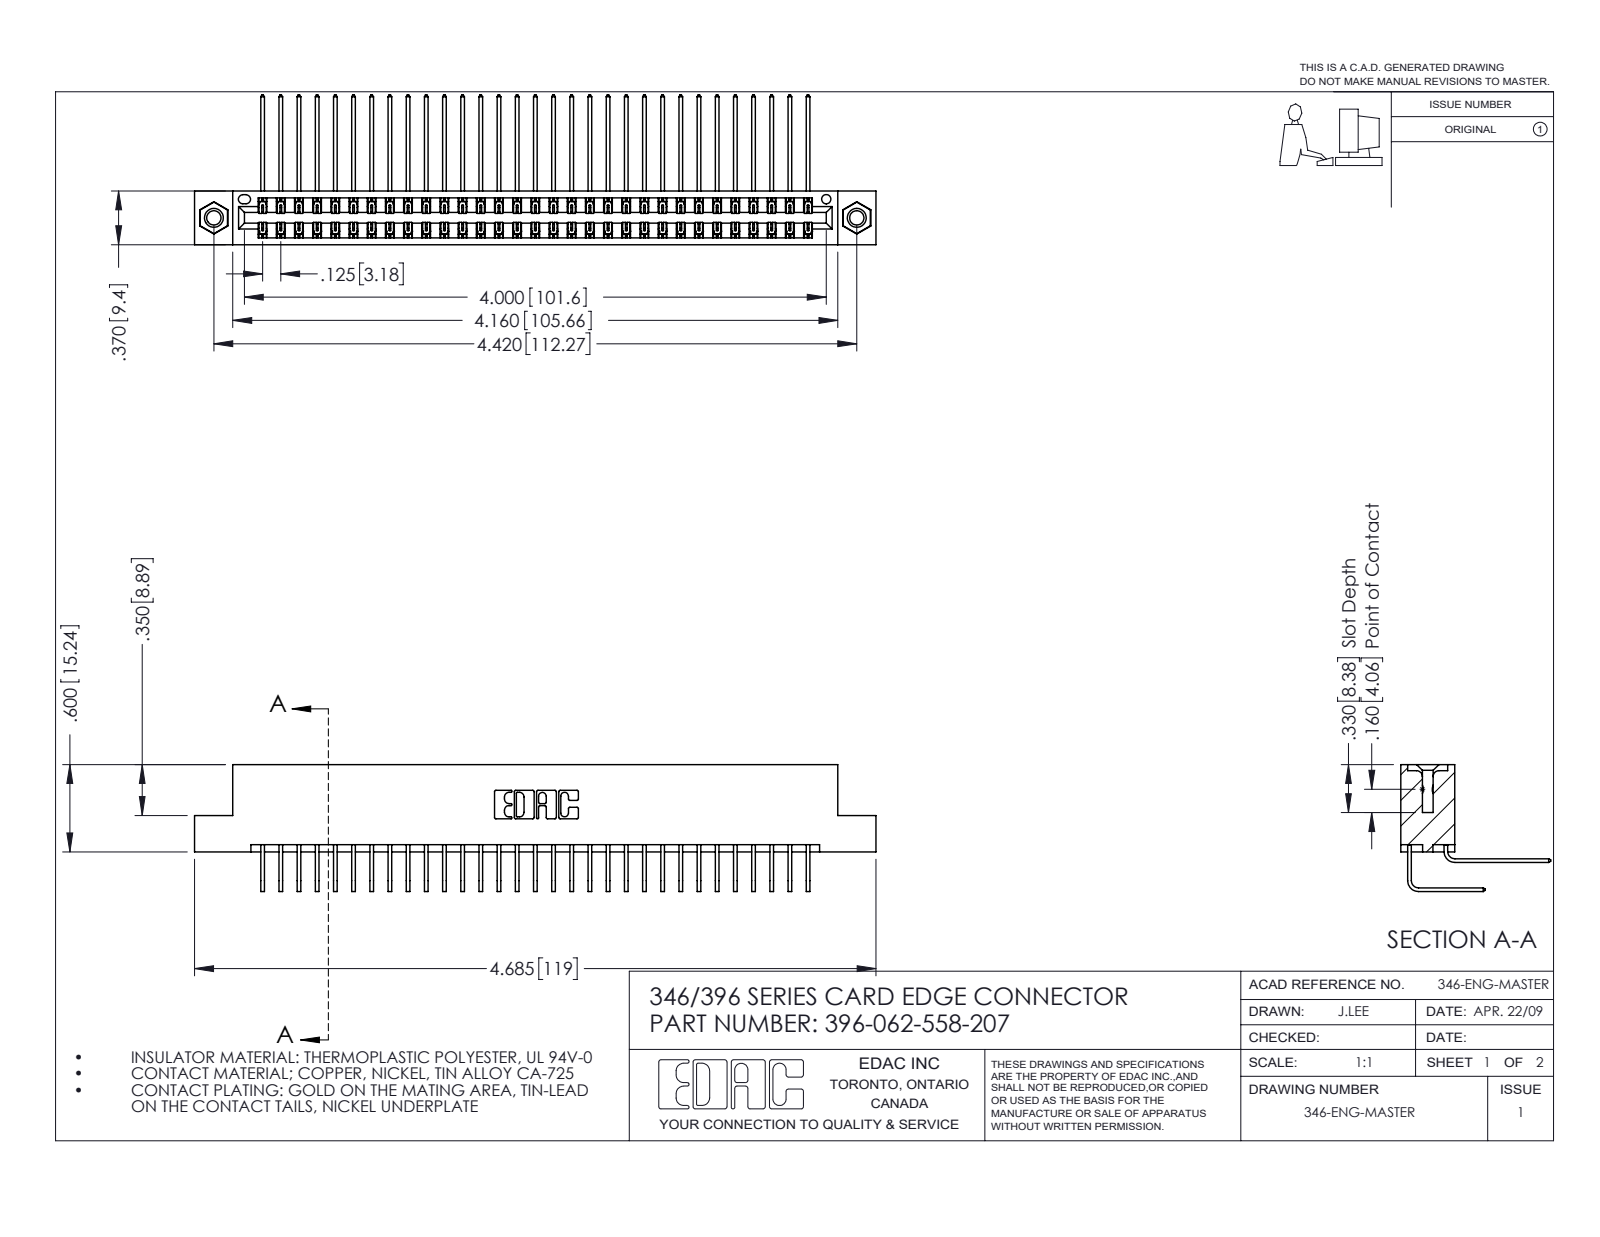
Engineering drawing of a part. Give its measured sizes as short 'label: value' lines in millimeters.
name: 346 Part_Flush Mounting Lugs - 0.156 Dia-TI; 345-250-001_345-250-005-103; 345-292-001_558 Tail - 2; 345-292-001_558 559 Tail - 1 (+1 more)
written by: SolidWorks 2016 (CONFIG_CONTROL_DESIGN)
unit: mm
bodies: 65 solids, 3530 faces (2402 planar, 1112 cylindrical, 16 other)
size: 119 × 26.2 × 22.2
volume: 11 900 mm³; area: 17 880 mm²
holes: 2× ⌀2.5, 2× ⌀3.2, 2× ⌀4, 1× ⌀1.6
bosses: 2× ⌀3.9
rounds: 93× R0.2, 22× R0.3, 6× R0.2, 6× R0.8, 3× R0.7, 2× R0.4, 2× R0.6, 2× R0.6
face distances: 1.2, 8.2, 0.6, 6.4, 9.4, 1.8, 7.6, 7, 3.8, 5.6
hole spacings: 6.2, 107, 112.3
